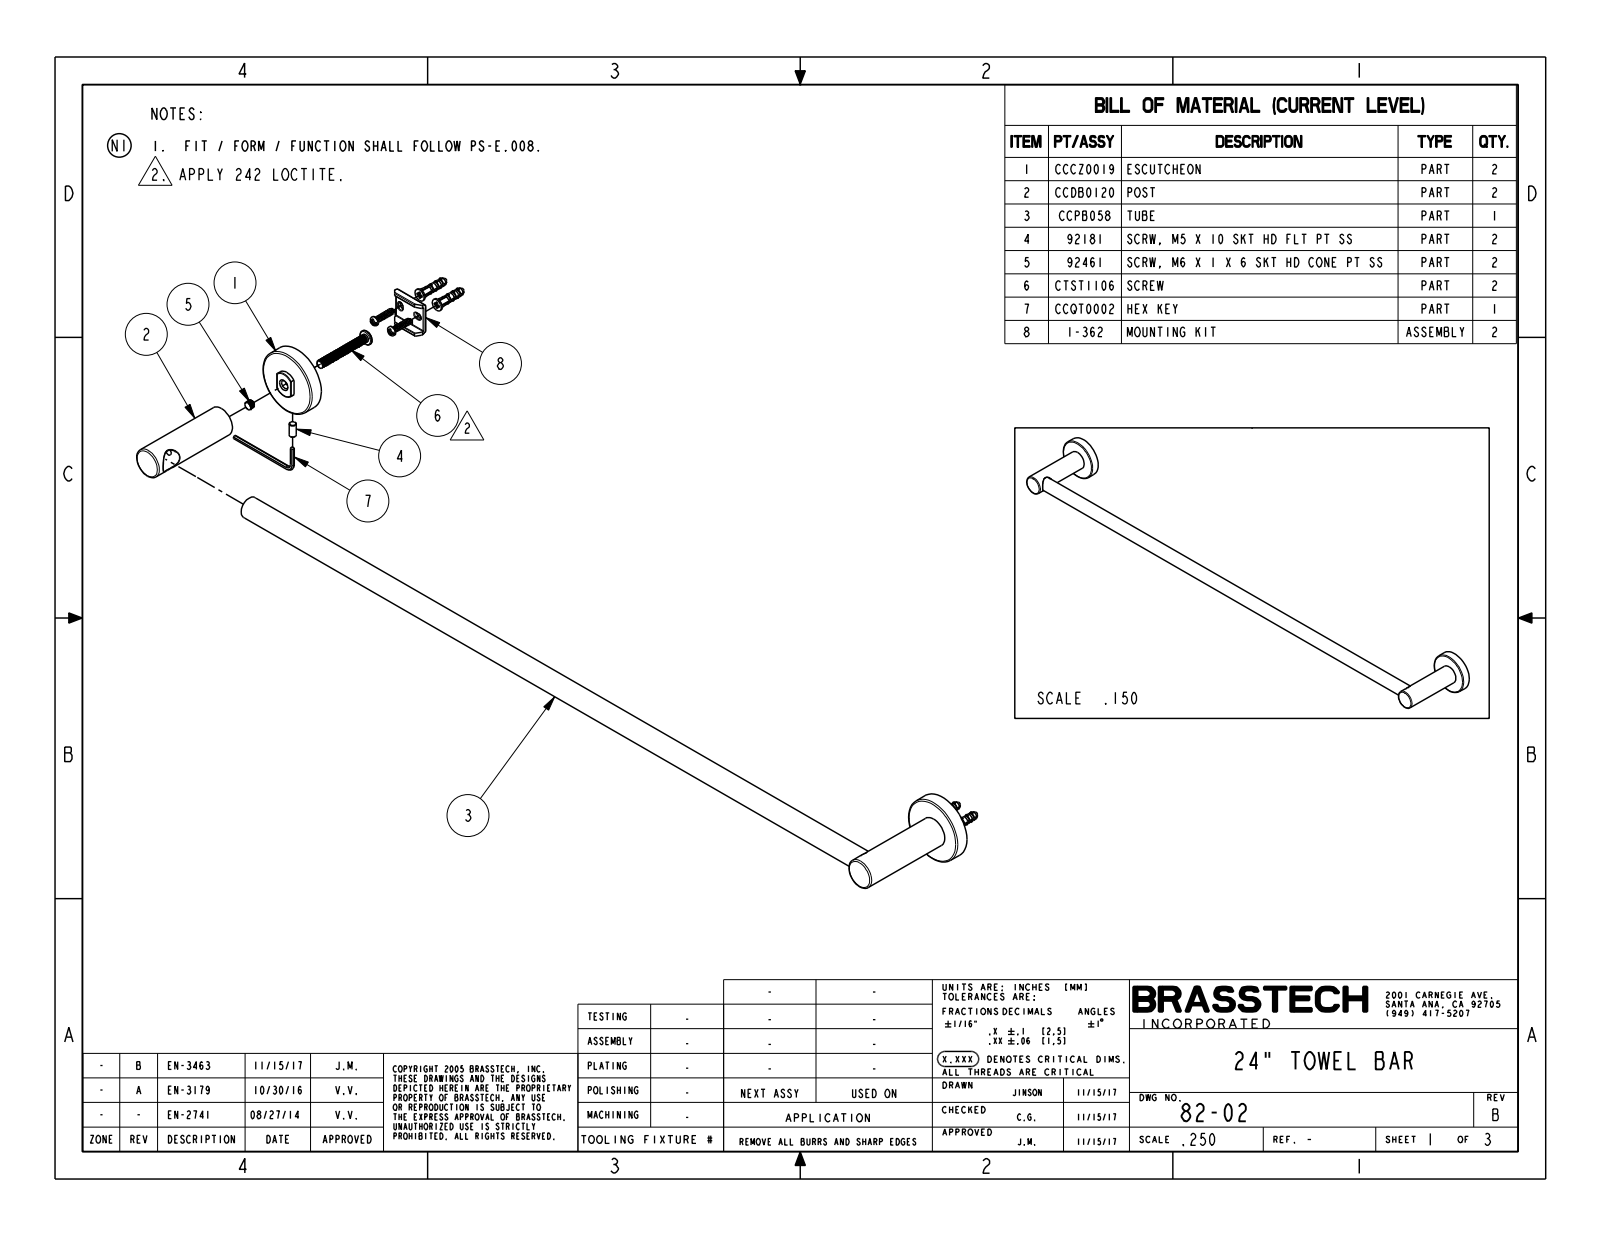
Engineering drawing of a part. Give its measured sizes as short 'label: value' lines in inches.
name: CCCZ0019; CCKT0030; CCDB0120; CCPB058 (+4 more)
written by: PRO/ENGINEER BY PARAMETRIC TECHNOLOGY CORPORATION, 2013150 (CONFIG_CONTROL_DESIGN)
unit: in
bodies: 13 solids, 736 faces (174 planar, 350 cylindrical, 212 other)
size: 25.912 × 3.268 × 1.897
volume: 4.758 in³; area: 150.3 in²
holes: 2× ⌀0.165, 2× ⌀0.205, 2× ⌀0.236, 2× ⌀0.244, 2× ⌀0.748, 1× ⌀0.547, 1× ⌀0.638
bosses: 3× ⌀0.236, 2× ⌀0.866, 2× ⌀0.197, 1× ⌀0.626
rounds: 88× R0.02, 8× R0.089, 4× R0.079, 2× R0.37, 2× R0.886
face distances: 0.079, 0.098, 0.295, 0.374, 0.197, 0.118, 0.276, 0.394, 3.248, 3.15
hole spacings: 24.016, 0.043, 24.059
